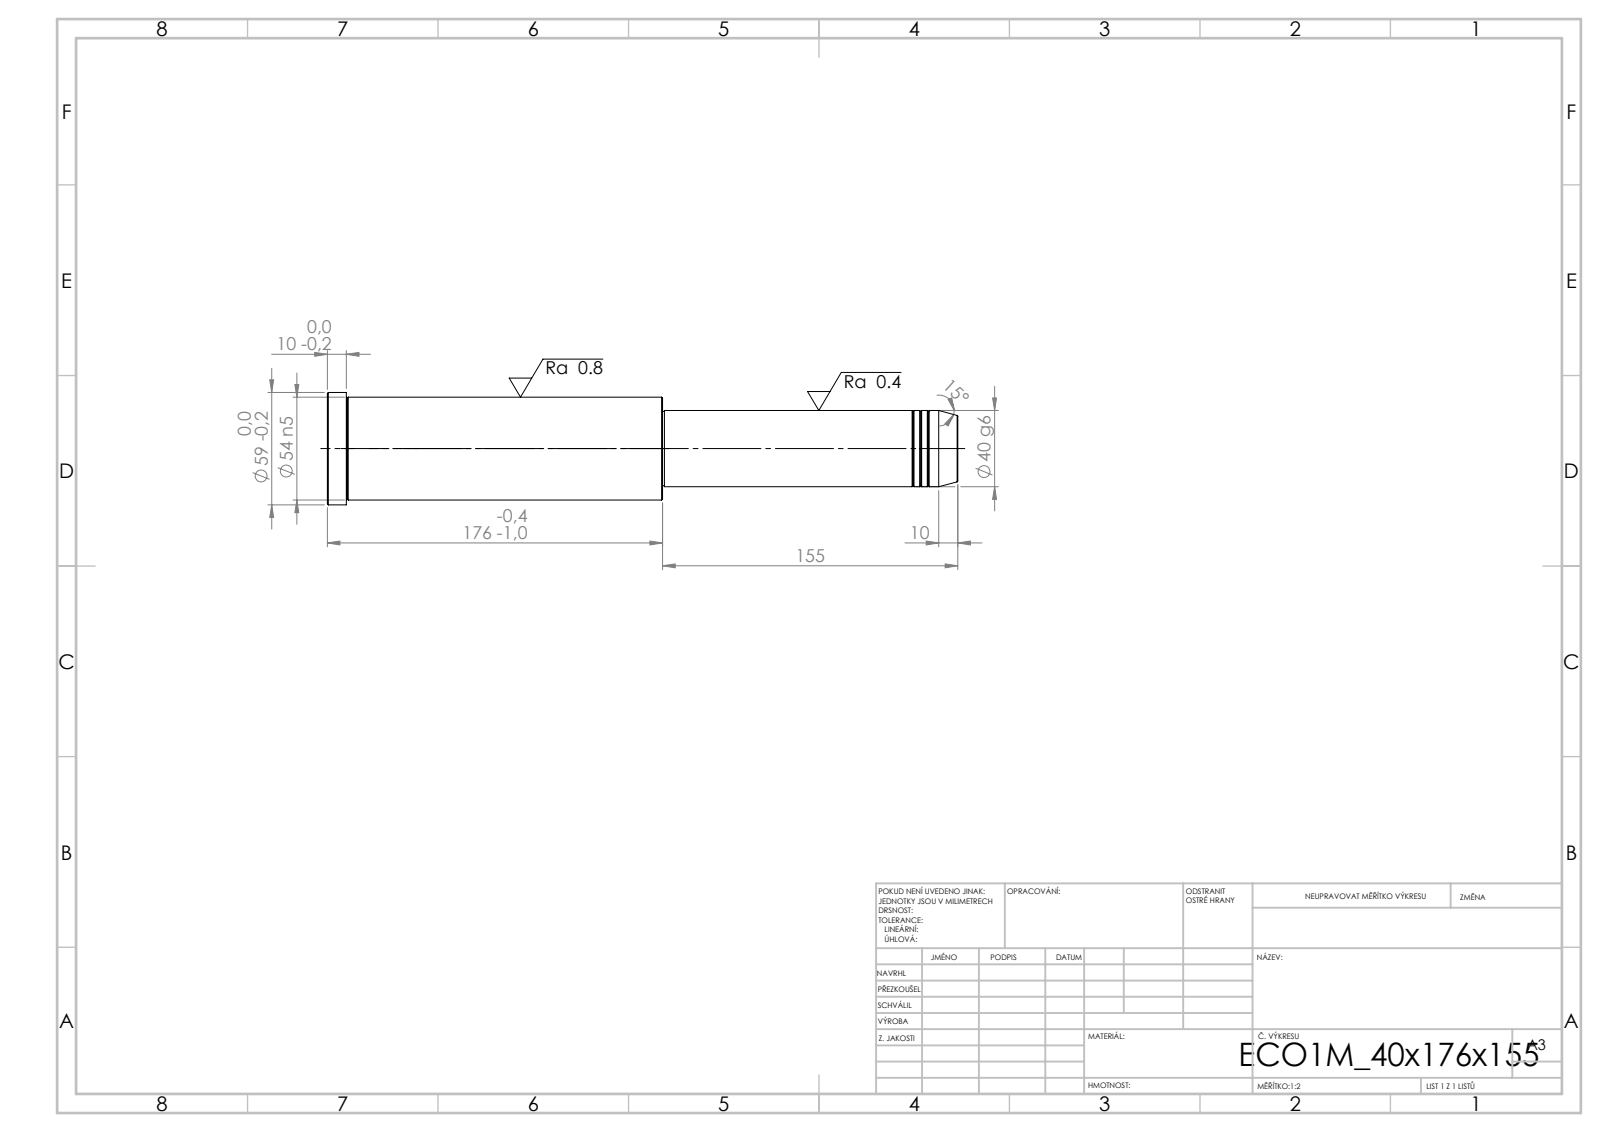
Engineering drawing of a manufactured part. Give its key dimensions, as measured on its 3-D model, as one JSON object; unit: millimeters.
{"step_written_by": "SolidWorks 2019 (CONFIG_CONTROL_DESIGN)", "units": "millimeters", "bodies": {"solids": 1, "faces": 43, "planar": 5, "cylindrical": 14, "other": 24}, "overall_size": [331, 59, 59], "volume_mm3": 600365, "surface_area_mm2": 54907, "round_bosses_or_shafts": [[59, 1], [54, 1], [40, 1], [39, 1]], "face_to_face_distances": [176, 155, 331, 321, 166, 10, 154, 1, 167, 177]}
